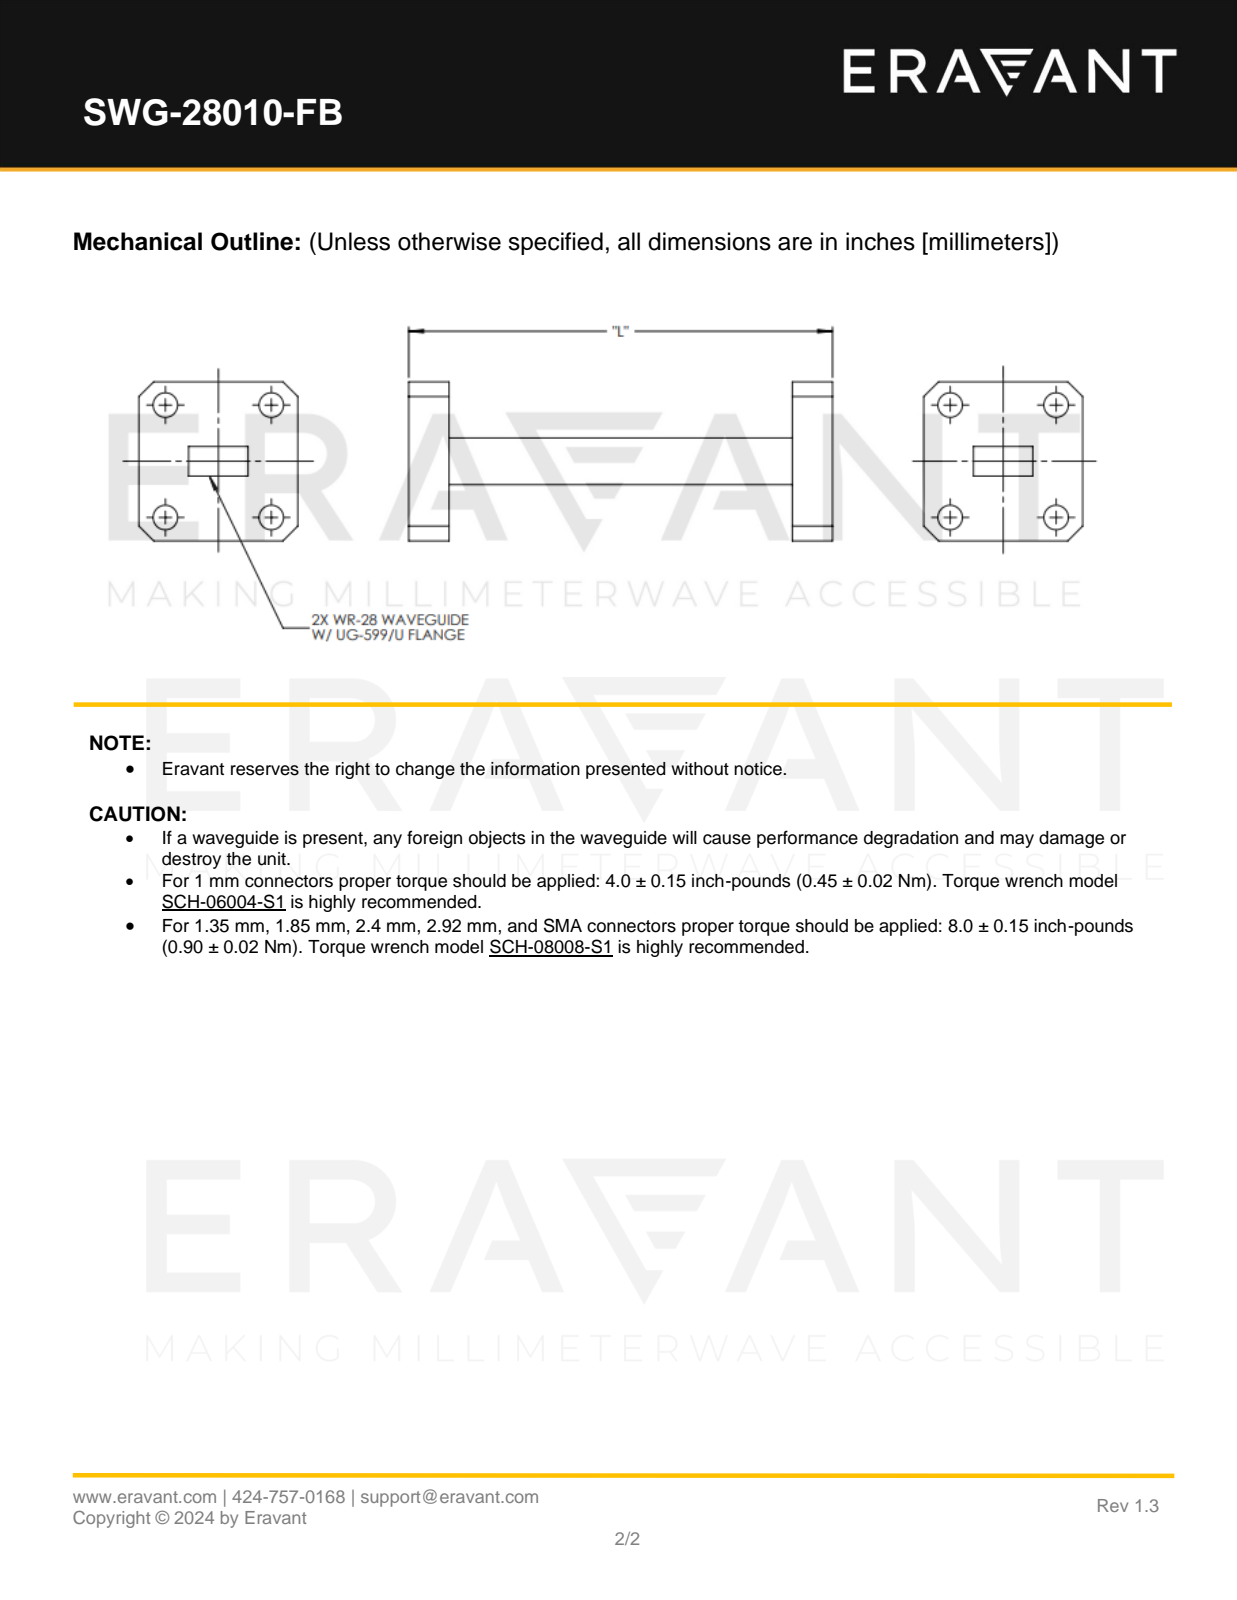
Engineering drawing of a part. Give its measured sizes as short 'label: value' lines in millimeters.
name: SWG-28010-FB
written by: SolidWorks 2021 (CONFIG_CONTROL_DESIGN)
unit: mm
bodies: 1 solid, 50 faces (34 planar, 16 cylindrical, 0 other)
size: 25.4 × 19.1 × 19.1
volume: 3 970 mm³; area: 2 743 mm²
holes: 4× ⌀2.9
face distances: 4.8, 20.6, 25.4, 15.7, 19.1, 5, 14.1, 6.7, 12.3, 5.6
hole spacings: 12.7, 13.5, 18.5
